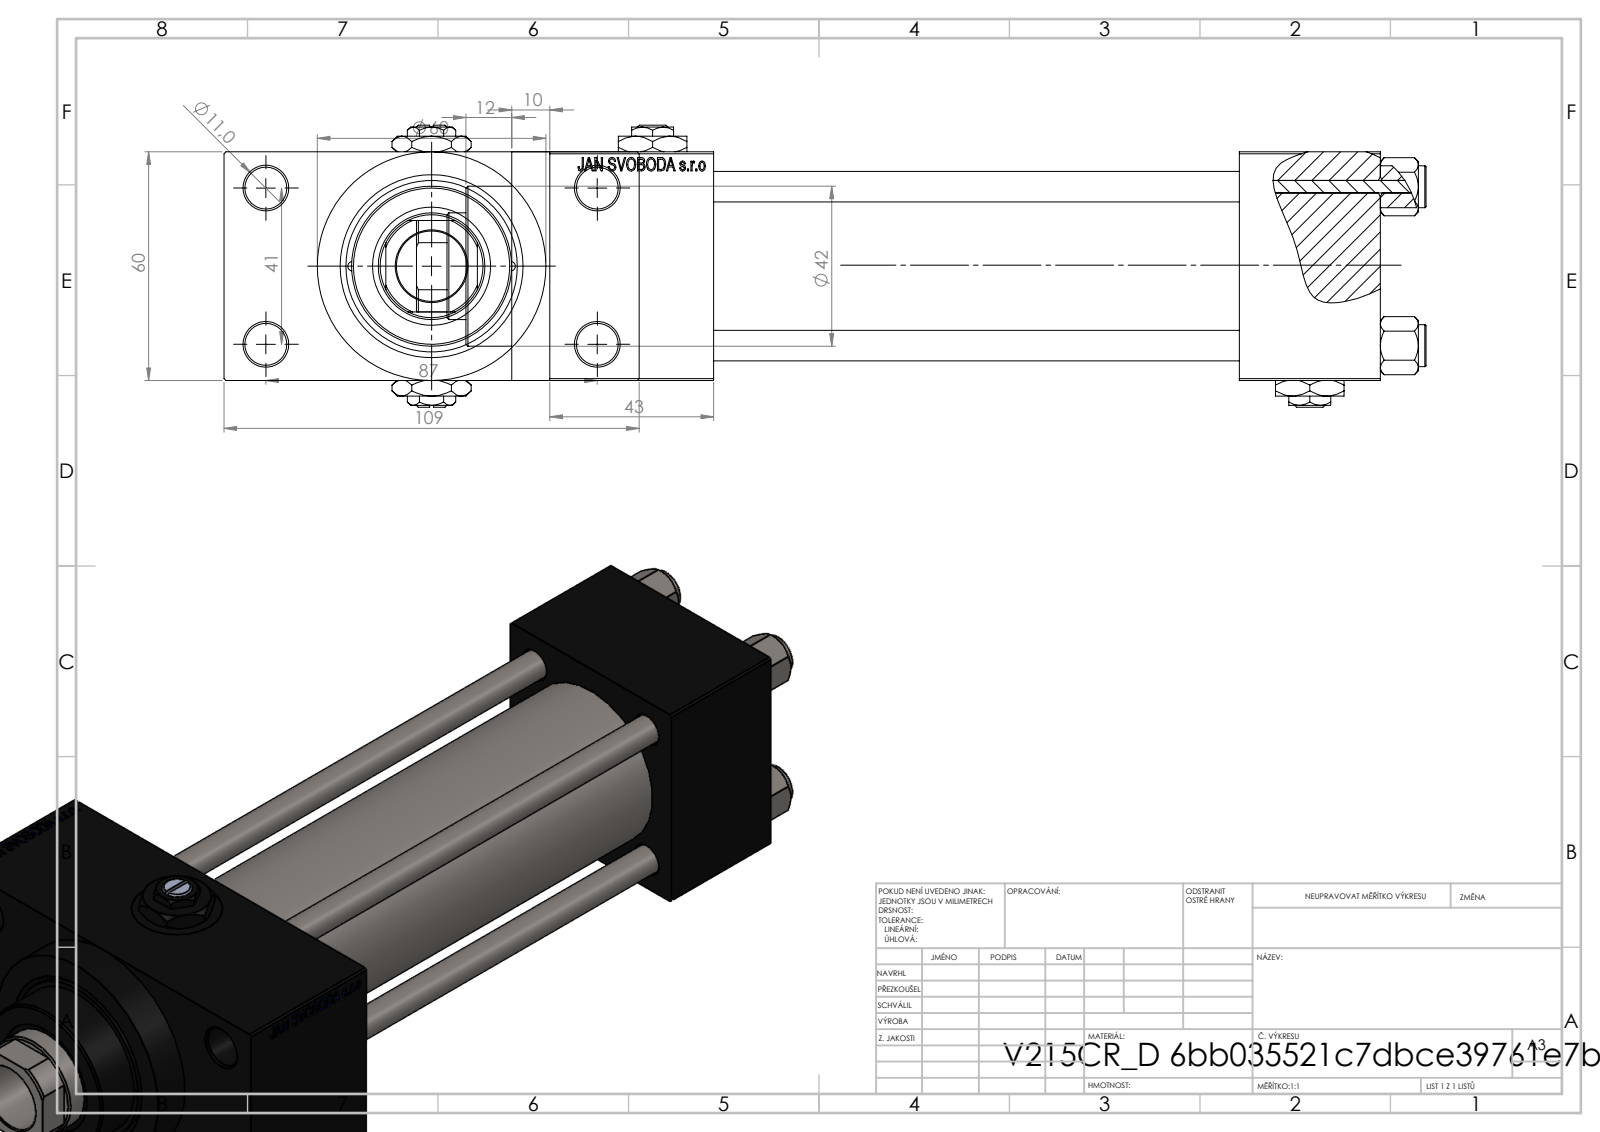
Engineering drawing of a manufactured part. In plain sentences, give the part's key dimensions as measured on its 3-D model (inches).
The part is named "NUT_M5_D; V215CR_D_TYCINKA; V215CR_D_Body; V215_VC_A (+2 more)". Its 3-D file was written by "SolidWorks 2019 (CONFIG_CONTROL_DESIGN)". It is 13 solids with 1199 faces: 546 planar, 93 cylindrical and 560 other. Overall it measures 10.433 by 4.291 by 2.913 inches. Its volume is 38.72 cubic inches and its surface area 257.8 square inches. Round holes: 4 of diameter 0.315, 4 of diameter 0.433, 2 of diameter 0.098, 2 of diameter 0.276, 2 of diameter 0.656, 2 of diameter 0.945, 1 of diameter 0.728, 1 of diameter 1.102, 1 of diameter 1.22, 1 of diameter 1.575, 1 of diameter 1.772. Round bosses or shafts: 4 of diameter 0.433, 1 of diameter 2.362, 1 of diameter 1.811, 1 of diameter 1.654. Partial cylindrical surfaces (rounded edges, fillets, slot ends): 1 of radius 0.531. The main face-to-face distances are 2.362, 0.965, 3.327, 5.433, 1.457, 6.89, 8.583, 7.126, 1.693, 4.291. The hole center spacings are 0.821, 0.892, 1.161, 1.206, 1.642, 1.832, 1.856, 1.893.
